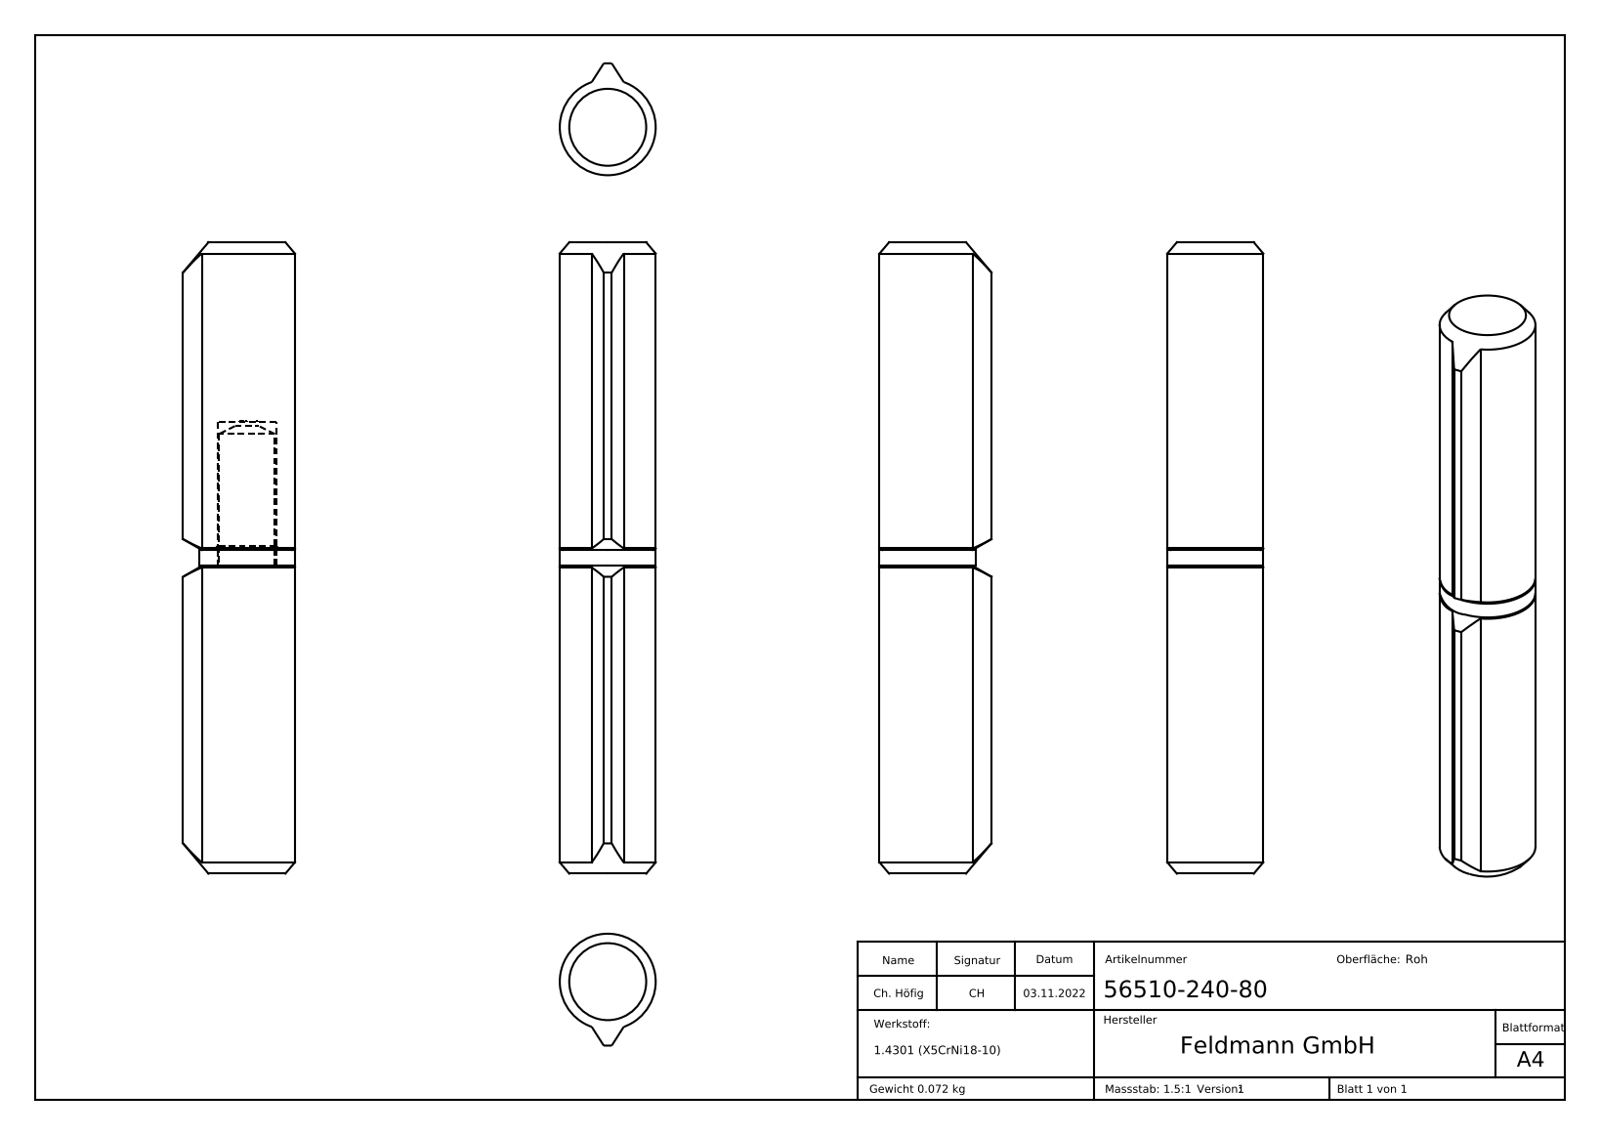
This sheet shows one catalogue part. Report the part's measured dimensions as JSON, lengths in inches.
{"part_name": "56510-240 Teil1_56510-240-80 Teil1; 56510-240-80; 56510-240 Teil3_56510-240-80 Teil3; 56510-240 Teil2_56510-240-80 Teil2", "step_written_by": "SolidWorks 2018 (CONFIG_CONTROL_DESIGN)", "units": "inches", "bodies": {"solids": 3, "faces": 324, "planar": 169, "cylindrical": 6, "other": 149}, "overall_size": [3.11, 0.551, 0.472], "volume_in3": 0.557, "surface_area_in2": 6.913, "round_holes": [[0.287, 1]], "round_bosses_or_shafts": [[0.472, 1], [0.276, 1]], "face_to_face_distances": [1.516, 1.594, 0.079, 3.11, 2.224, 0.709, 0.63, 0.886, 0.02, 2.205]}
